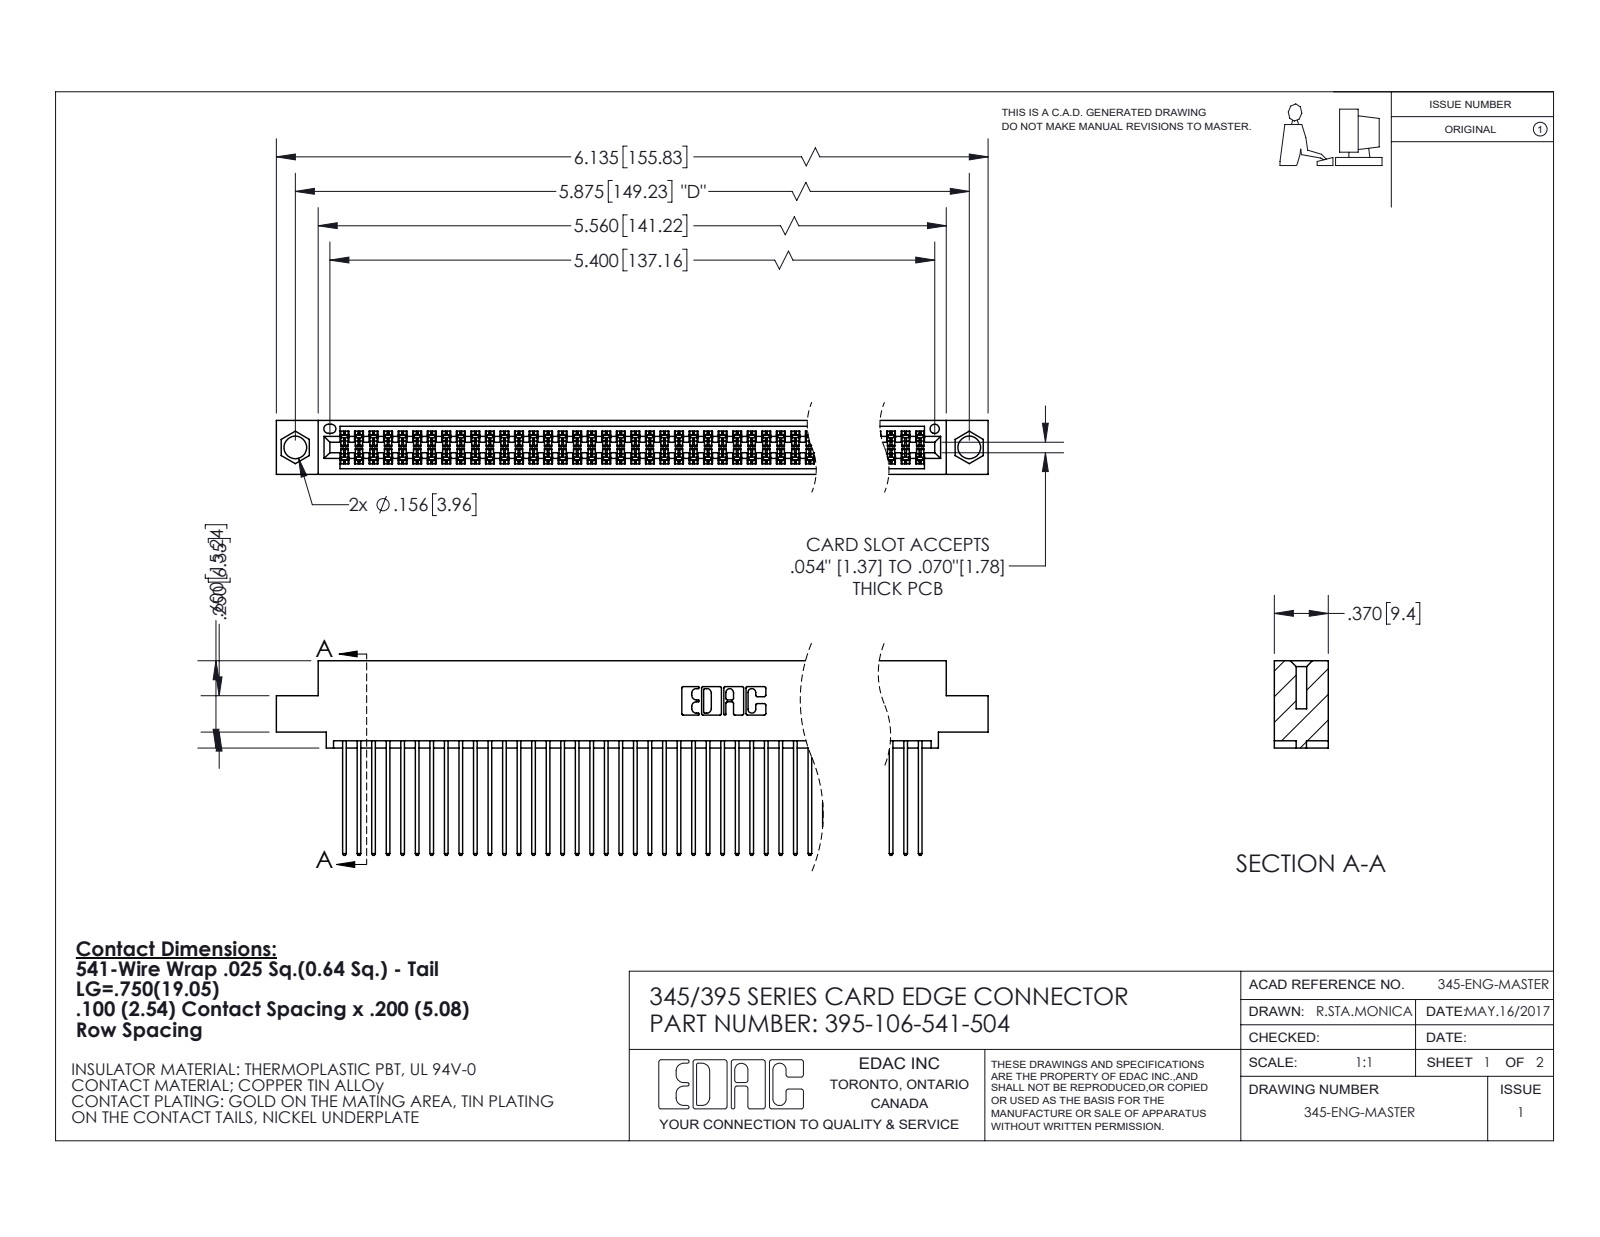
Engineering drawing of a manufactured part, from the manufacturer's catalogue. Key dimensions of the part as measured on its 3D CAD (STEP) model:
Part name (STEP PRODUCT): 345-292-001_345-293-141; 395-106-541-504; 345 Part_0.110 Offset - 0.156 Dia-TI
STEP written by: SolidWorks 2020 (CONFIG_CONTROL_DESIGN)
Units: inches
Bodies: 107 solids, 5444 faces (3596 planar, 1848 cylindrical, 0 other)
Overall size (bounding box): 6.135 × 1.337 × 0.37
Volume: 0.956 in³ · Surface area: 40.57 in²
Round holes (diameter × count): ⌀0.156 ×2, ⌀0.064 ×1
Partial cylindrical surfaces — rounded edges, fillets, slot ends (radius × count): R0.006 ×159, R0.01 ×106, R0.01 ×22, R0.007 ×6, R0.031 ×6, R0.026 ×3, R0.014 ×2, R0.019 ×2
Main face-to-face distances: 0.298, 0.072, 0.2, 0.098, 0.272, 0.025, 0.225, 0.37, 0.175, 0.149
Hole centre spacings: 0.27, 5.639, 5.875
